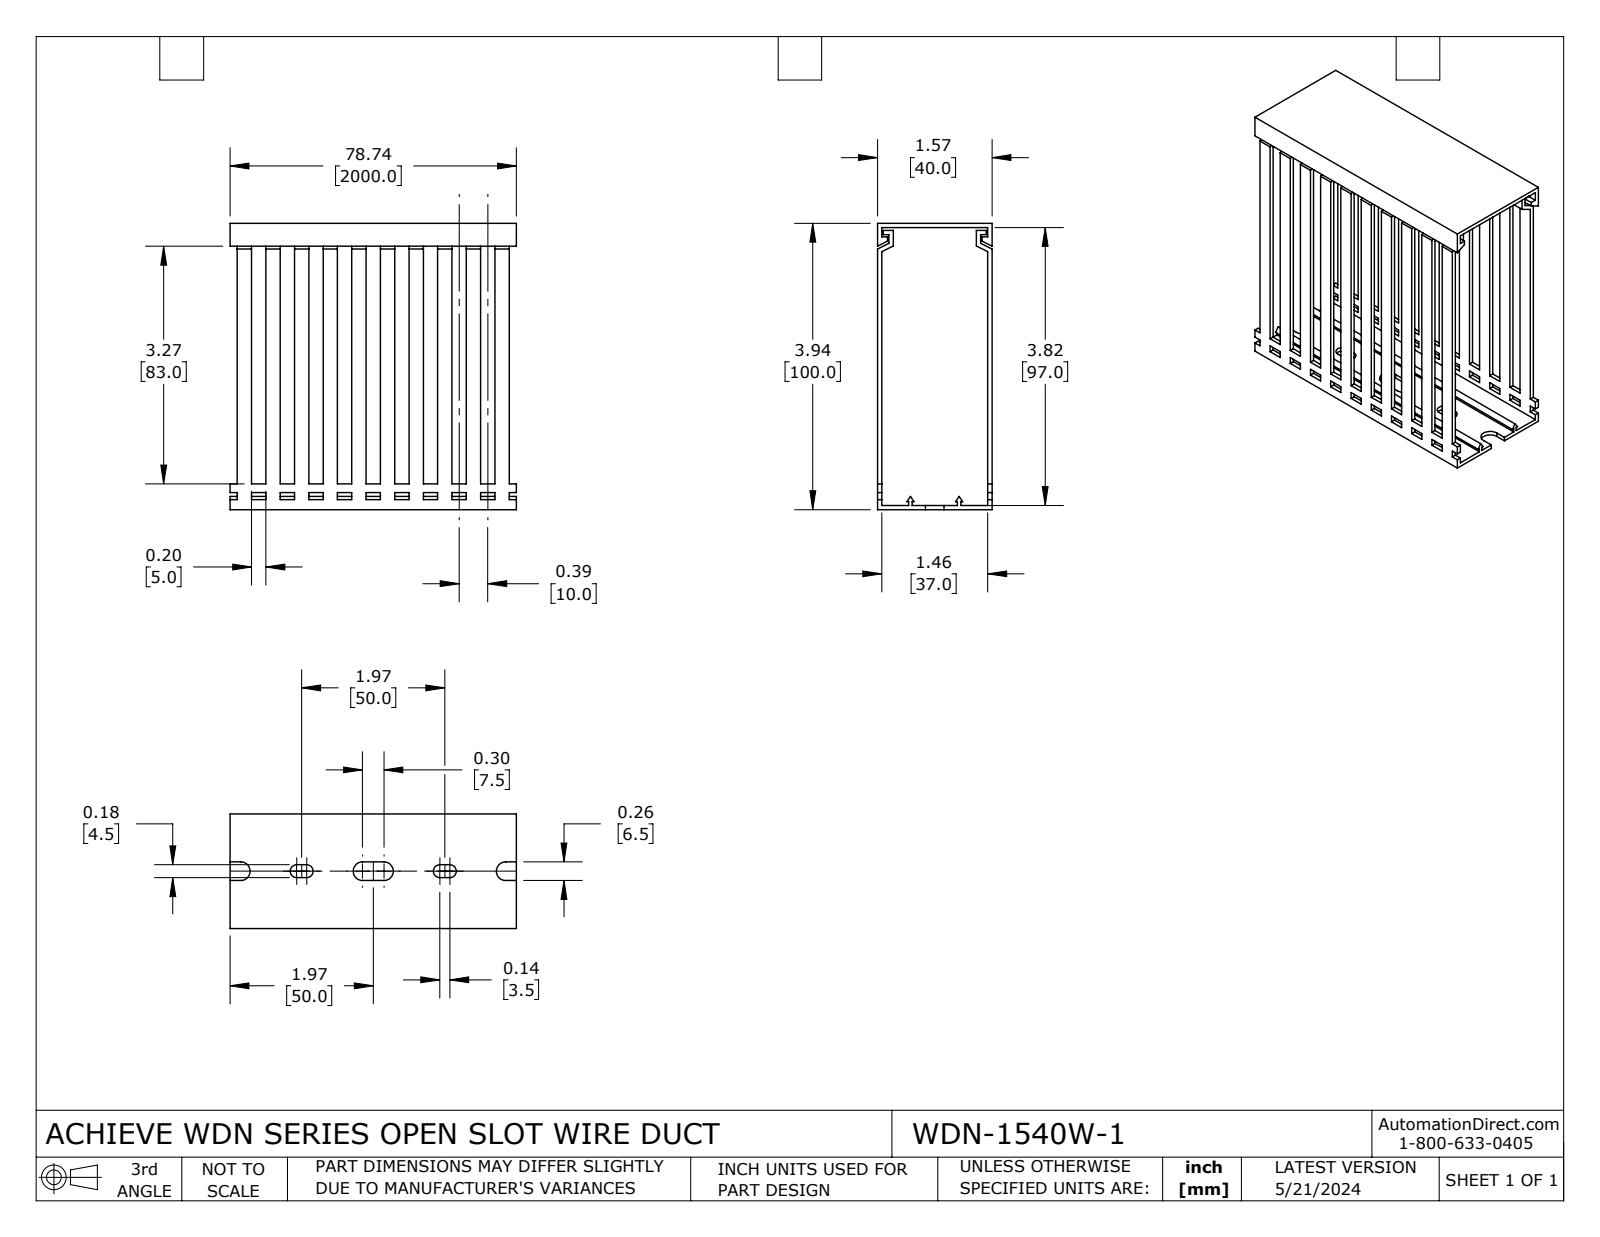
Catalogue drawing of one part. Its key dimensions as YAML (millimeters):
part_name: "WDN-1540W-1"
step_written_by: "SolidWorks 2023 (CONFIG_CONTROL_DESIGN)"
units: millimeters
bodies: {solids: 2, faces: 350, planar: 338, cylindrical: 12, other: 0}
overall_size: [100, 100, 40]
volume: 30890
surface_area: 48320
partial_cylinders:
  - {radius: 2.3, count: 4}
  - {radius: 3.3, count: 4}
face_to_face_distances: [1.5, 38.5, 40, 98.5, 5, 10, 37, 15, 20, 25]
